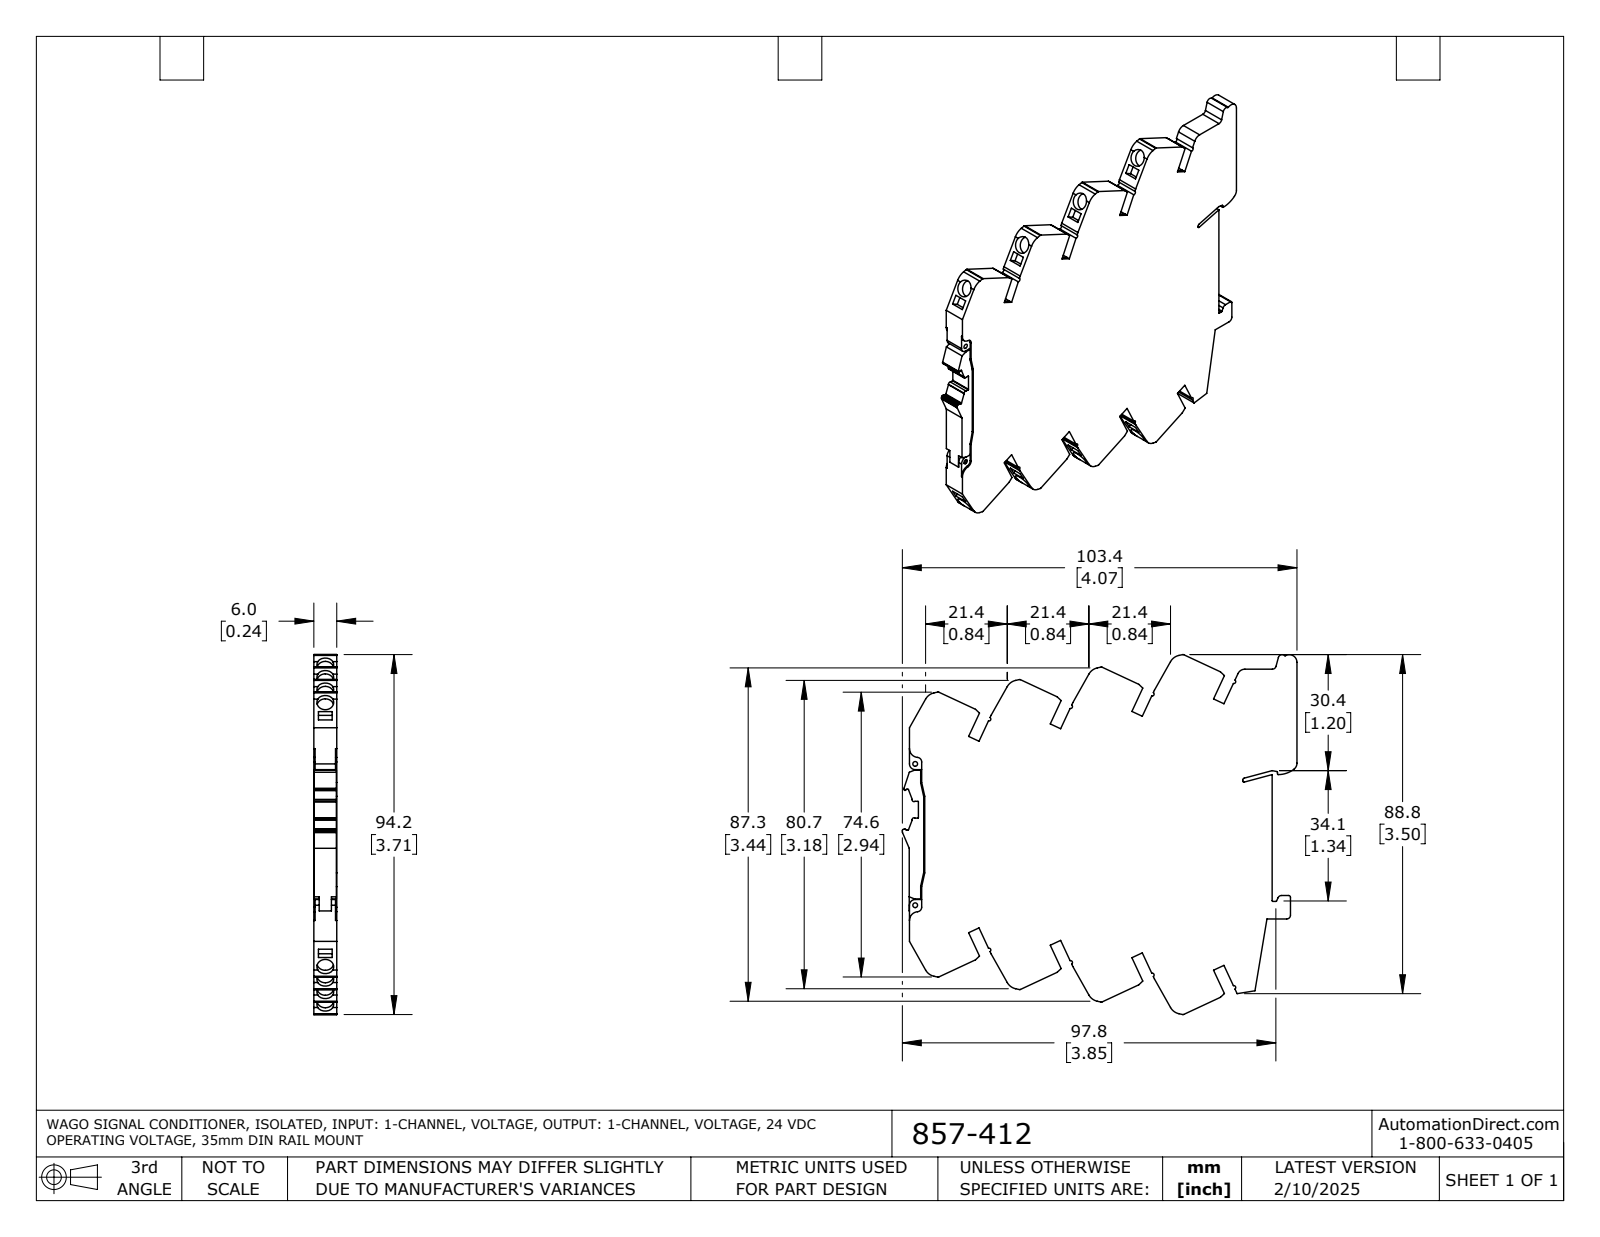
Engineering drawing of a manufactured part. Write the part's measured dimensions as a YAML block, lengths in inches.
part_name: "857-412"
step_written_by: "SolidWorks 2021 (AUTOMOTIVE_DESIGN)"
units: inches
bodies: {solids: 1, faces: 317, planar: 219, cylindrical: 98, other: 0}
overall_size: [4.069, 3.711, 0.236]
volume: 2.681
surface_area: 29.86
round_holes:
  - {diameter: 0.173, count: 8}
  - {diameter: 0.049, count: 2}
partial_cylinders:
  - {radius: 0.02, count: 12}
  - {radius: 0.008, count: 11}
  - {radius: 0.016, count: 8}
  - {radius: 0.132, count: 8}
  - {radius: 0.039, count: 4}
  - {radius: 0.012, count: 3}
  - {radius: 0.079, count: 3}
  - {radius: 0.018, count: 2}
face_to_face_distances: [0.236, 0.708, 0.67, 0.473, 0.232, 0.472, 0.118, 0.945, 1.417, 0.256]
hole_center_spacings: [0.526, 0.525, 1.051, 1.051, 1.052, 1.457, 1.576, 1.577]
